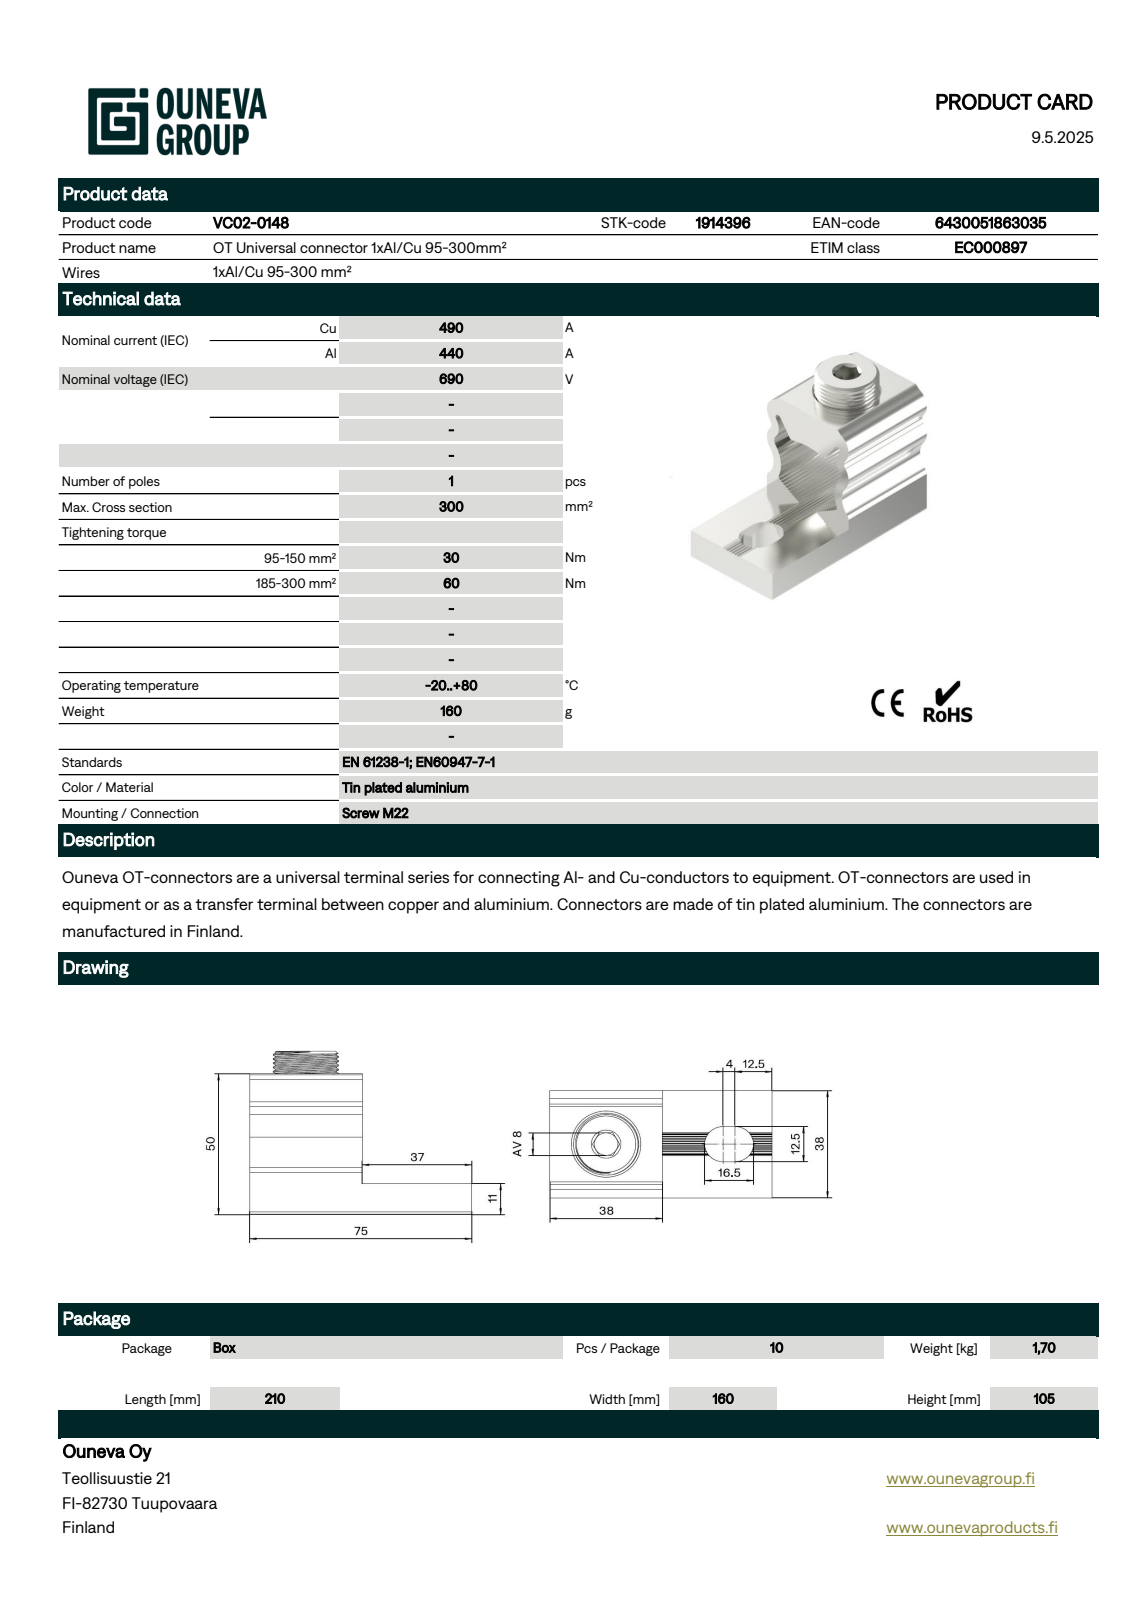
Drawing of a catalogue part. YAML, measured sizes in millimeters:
part_name: "Liitinrunko OT 1x300"
step_written_by: "Creo Elements/Direct Modeling 20.6A 14-Oct-2023 (C) Parametric Technology GmbH (AUTOMOTIVE_DESIGN)"
units: millimeters
bodies: {solids: 1, faces: 373, planar: 173, cylindrical: 192, other: 8}
overall_size: [75, 57.97, 38.08]
volume: 58923
surface_area: 18839
round_bosses_or_shafts:
  - {diameter: 22, count: 1}
partial_cylinders:
  - {radius: 0.3, count: 63}
  - {radius: 0.3, count: 51}
  - {radius: 1.19, count: 8}
  - {radius: 2.38, count: 4}
  - {radius: 1.5, count: 2}
  - {radius: 2.86, count: 2}
  - {radius: 5.71, count: 2}
  - {radius: 5.83, count: 2}
face_to_face_distances: [38.08, 38, 39, 0.86, 1.72, 37, 75, 3.45, 8, 2.58]
